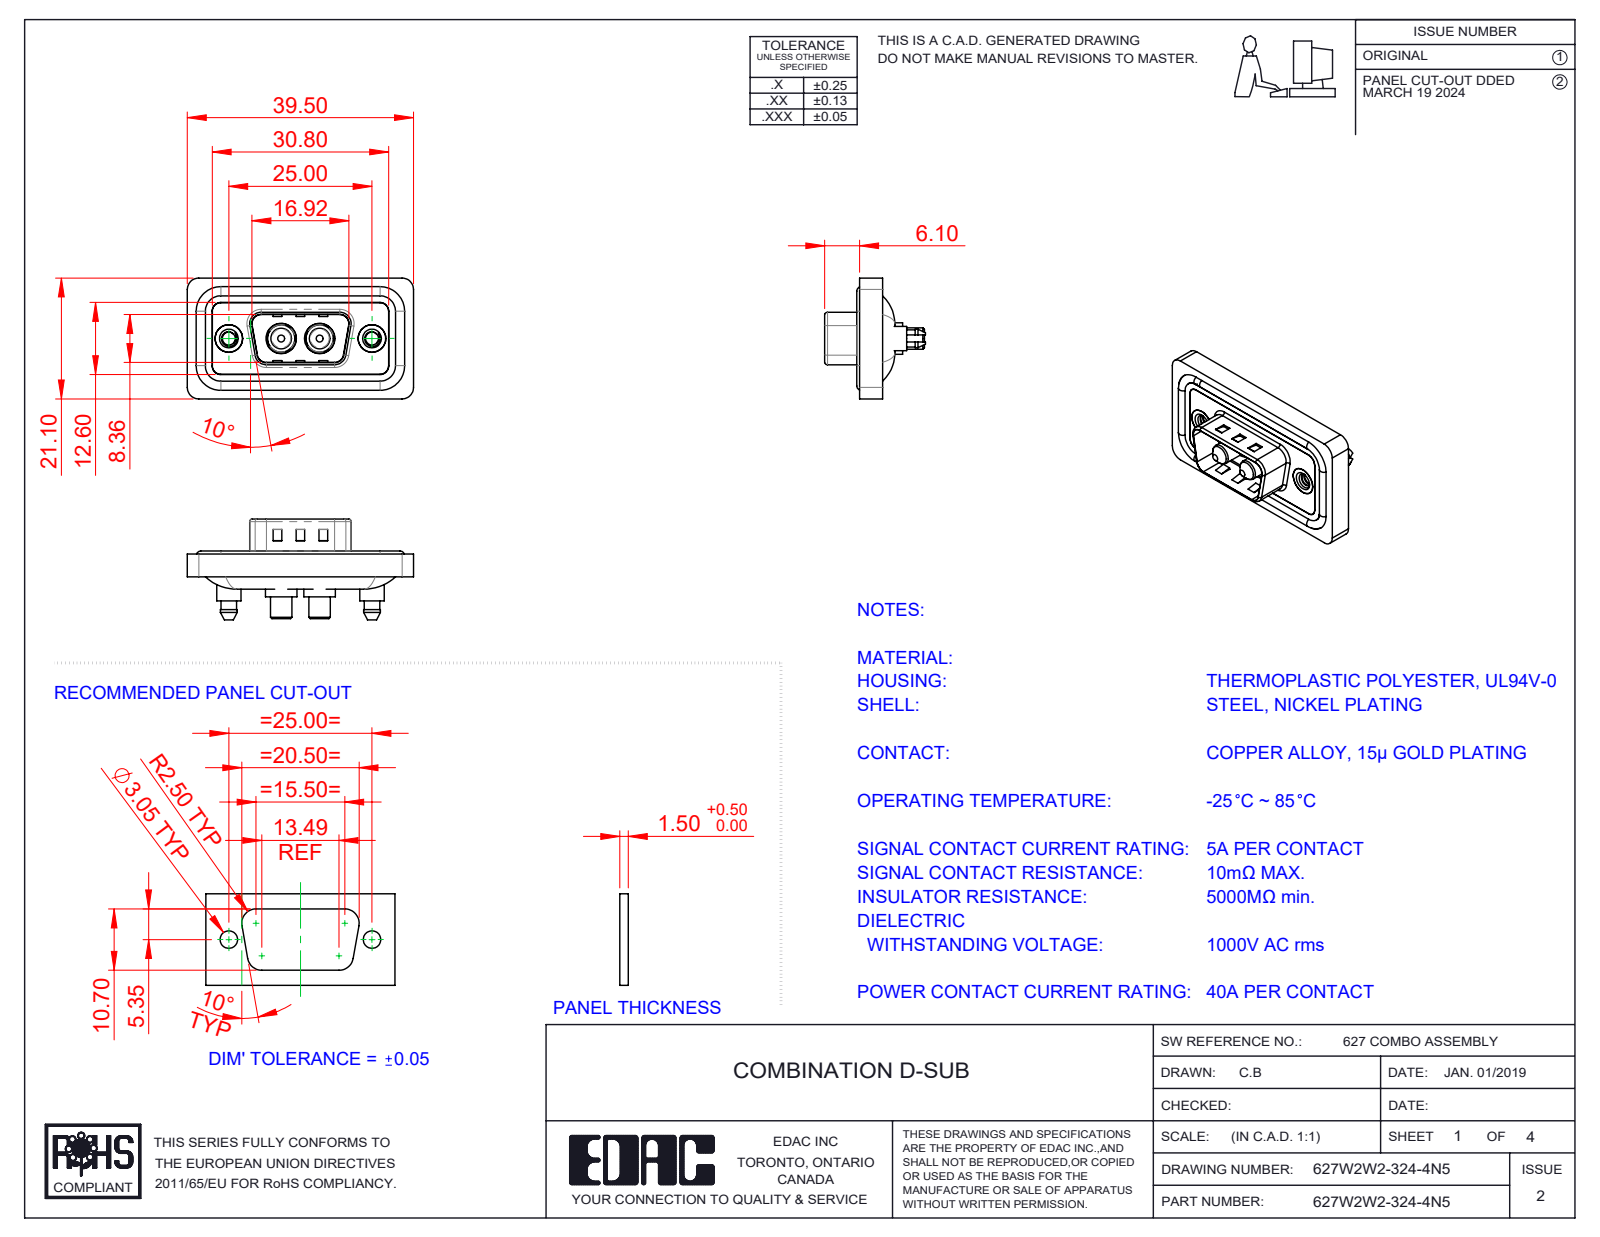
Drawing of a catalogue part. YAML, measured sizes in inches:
part_name: "627Combo Waterproof Housing_09 Contacts; Power Pin_40A S; 627W2W2-324-4N5; 627Combo Threaded Boardlock_5 (+3 more)"
step_written_by: "SolidWorks 2023 (CONFIG_CONTROL_DESIGN)"
units: inches
bodies: {solids: 11, faces: 539, planar: 181, cylindrical: 250, other: 108}
overall_size: [1.555, 0.831, 0.693]
volume: 0.283
surface_area: 11.38
round_holes:
  - {diameter: 0.089, count: 2}
  - {diameter: 0.157, count: 2}
  - {diameter: 0.189, count: 2}
  - {diameter: 0.191, count: 2}
  - {diameter: 0.197, count: 2}
  - {diameter: 0.209, count: 2}
round_bosses_or_shafts:
  - {diameter: 0.063, count: 4}
  - {diameter: 0.217, count: 2}
  - {diameter: 0.213, count: 2}
  - {diameter: 0.205, count: 2}
  - {diameter: 0.193, count: 2}
  - {diameter: 0.187, count: 2}
  - {diameter: 0.167, count: 2}
  - {diameter: 0.148, count: 2}
partial_cylinders:
  - {radius: 0.059, count: 24}
  - {radius: 0.079, count: 18}
  - {radius: 0.063, count: 10}
  - {radius: 0.02, count: 8}
  - {radius: 0.01, count: 4}
  - {radius: 0.024, count: 4}
  - {radius: 0.026, count: 4}
  - {radius: 0.035, count: 4}
face_to_face_distances: [0.016, 0.043, 0.114, 0.122, 0.02, 0.063, 0.059, 0.157, 0.028, 0.098]
hole_center_spacings: [0.36, 0.624, 0.265, 0.984]
